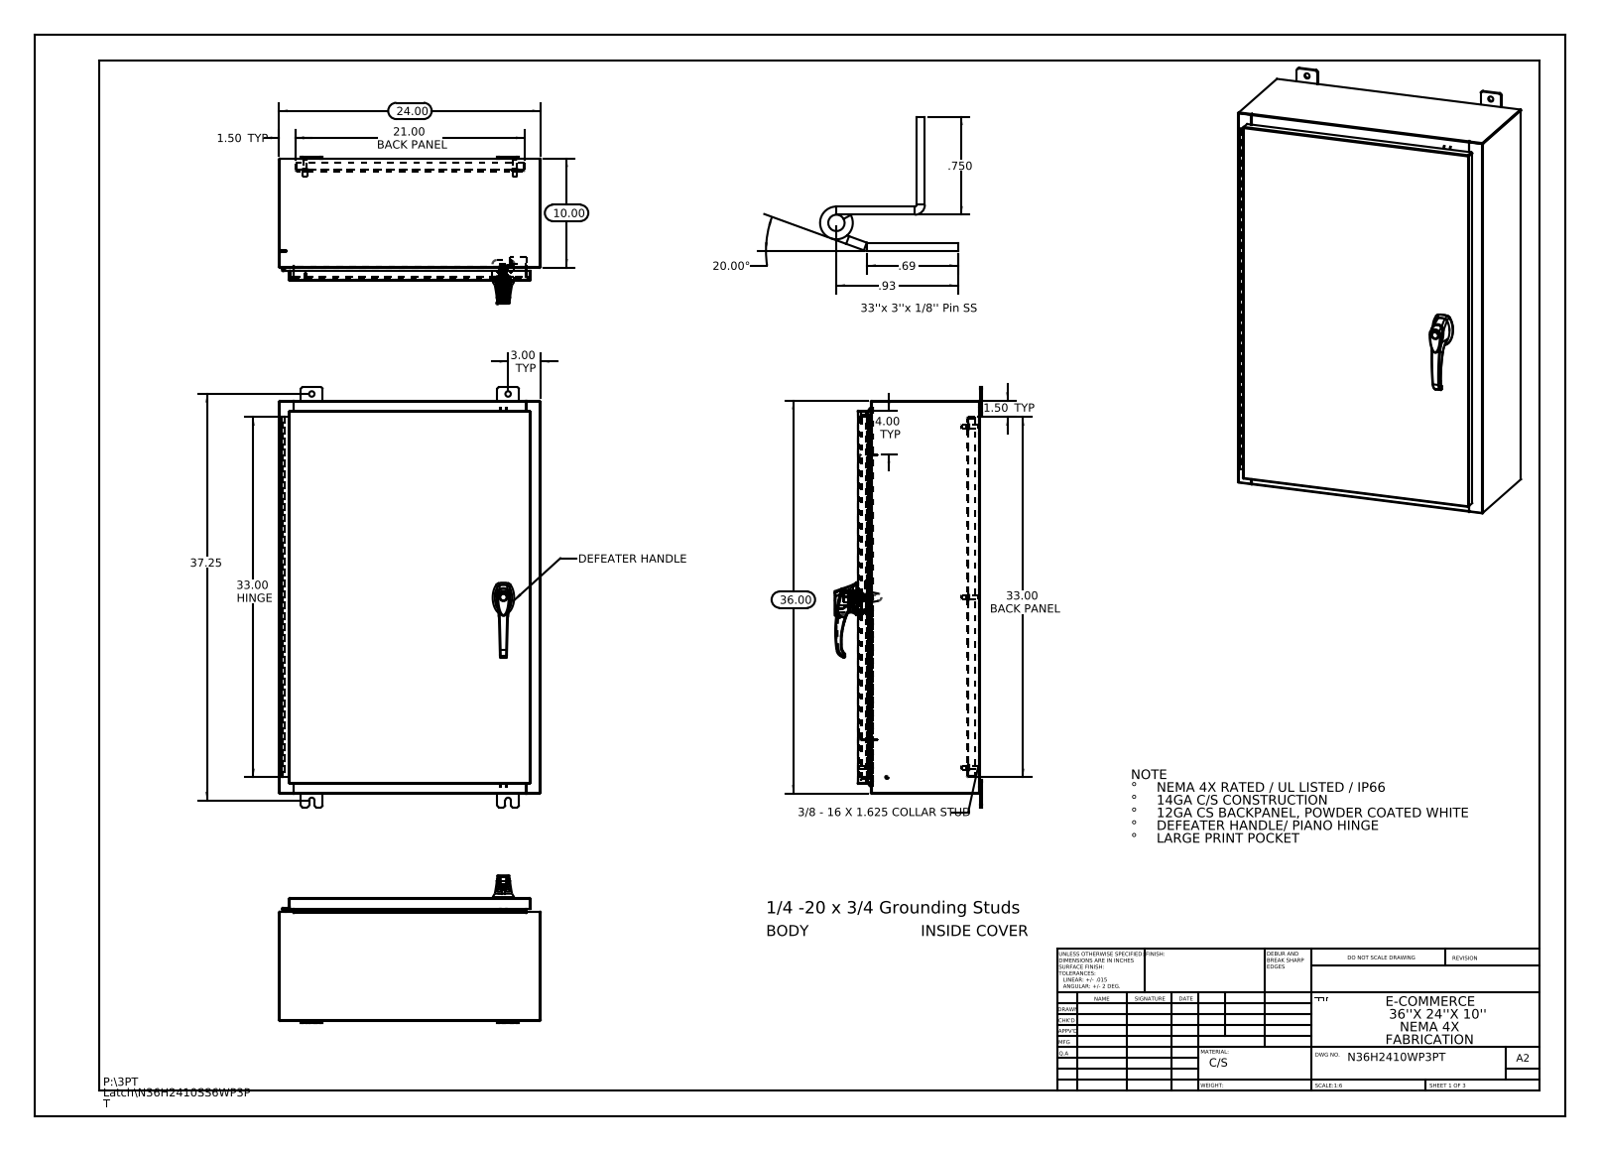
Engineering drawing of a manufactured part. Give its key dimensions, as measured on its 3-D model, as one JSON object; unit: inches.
{"part_name": "N36H2410SS6WP3PT Body; N36H2410SS6WP3PT Mounting Feet; N36H2410SS6WP3PT Backpanel; 022151 (+8 more)", "step_written_by": "SolidWorks 2013 (CONFIG_CONTROL_DESIGN)", "units": "inches", "bodies": {"solids": 33, "faces": 2770, "planar": 1035, "cylindrical": 1061, "other": 674}, "overall_size": [38.5, 24, 13.495], "volume_in3": 336.3, "surface_area_in2": 8336, "round_holes": [[0.5, 10], [0.25, 4], [0.138, 3], [0.161, 3], [0.079, 2], [0.203, 2], [0.313, 2], [0.437, 2], [0.125, 1], [0.125, 1], [0.197, 1], [0.276, 1]], "round_bosses_or_shafts": [[0.625, 6], [0.375, 6], [0.33, 6], [1.181, 1], [0.748, 1], [0.68, 1], [0.661, 1], [0.639, 1]], "partial_cylinders_radius": [[0.118, 37], [0.006, 33], [0.013, 24], [0.19, 24], [0.088, 18], [0.039, 15], [0.028, 12], [0.008, 6]], "face_to_face_distances": [0.075, 11.126, 0.104, 11.051, 11.201, 23.925, 1, 1.075, 10.051, 10.126], "hole_center_spacings": [11.363, 13.669, 15.625, 24.793, 19.25, 0.295, 0.625, 0.841]}
